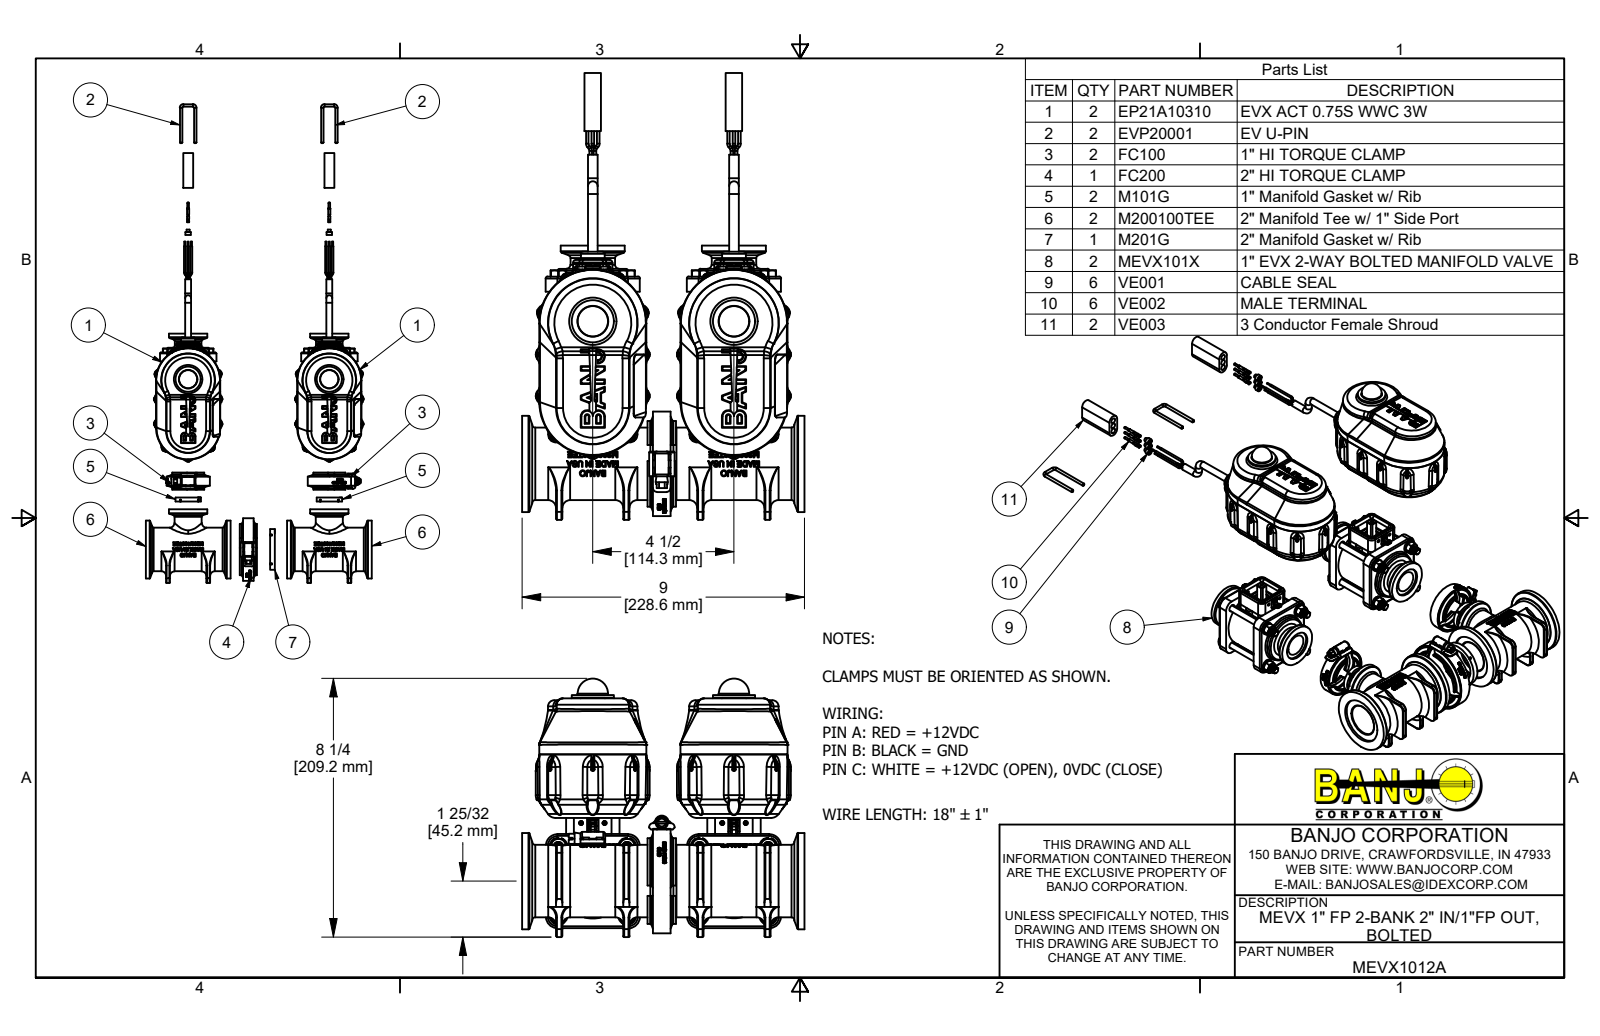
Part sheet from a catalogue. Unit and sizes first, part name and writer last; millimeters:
Units: millimetres
Overall size (bounding box): 361.5 × 228.6 × 209.2
Round holes (diameter × count): ⌀2.4 ×22, ⌀3.8 ×22, ⌀2 ×14, ⌀3.8 ×14, ⌀6.4 ×11, ⌀2.7 ×8, ⌀3.2 ×8, ⌀3.5 ×8, ⌀3.8 ×8, ⌀4.3 ×8, ⌀6.4 ×8, ⌀8.2 ×8
Round bosses / shafts (diameter × count): ⌀6.8 ×120, ⌀2 ×36, ⌀6.4 ×34, ⌀3.6 ×22, ⌀2.7 ×22, ⌀2.2 ×22, ⌀1.5 ×12, ⌀8 ×10
Partial cylindrical surfaces — rounded edges, fillets, slot ends (radius × count): R0.3 ×360, R1 ×290, R0.3 ×159, R0.8 ×133, R0.5 ×124, R0.1 ×94, R1.5 ×80, R2 ×56
Main face-to-face distances: 2.5, 114.3, 65.2, 12.2, 1.5, 5.4, 3.8, 60.1, 25.3, 89
Hole centre spacings: 114.3, 39.3, 55.6, 68.3, 127.1, 19.1, 24, 31.2
Volume: 2 234 000 mm³ · Surface area: 954 800 mm²
Bodies: 214 solids, 25029 faces (6604 planar, 7326 cylindrical, 11099 other)
Part name (STEP PRODUCT): MEVX1012A; EP21A10310; EP10310; IRF4905 (+8 more)
STEP written by: Autodesk Inventor 2019 (AUTOMOTIVE_DESIGN)
